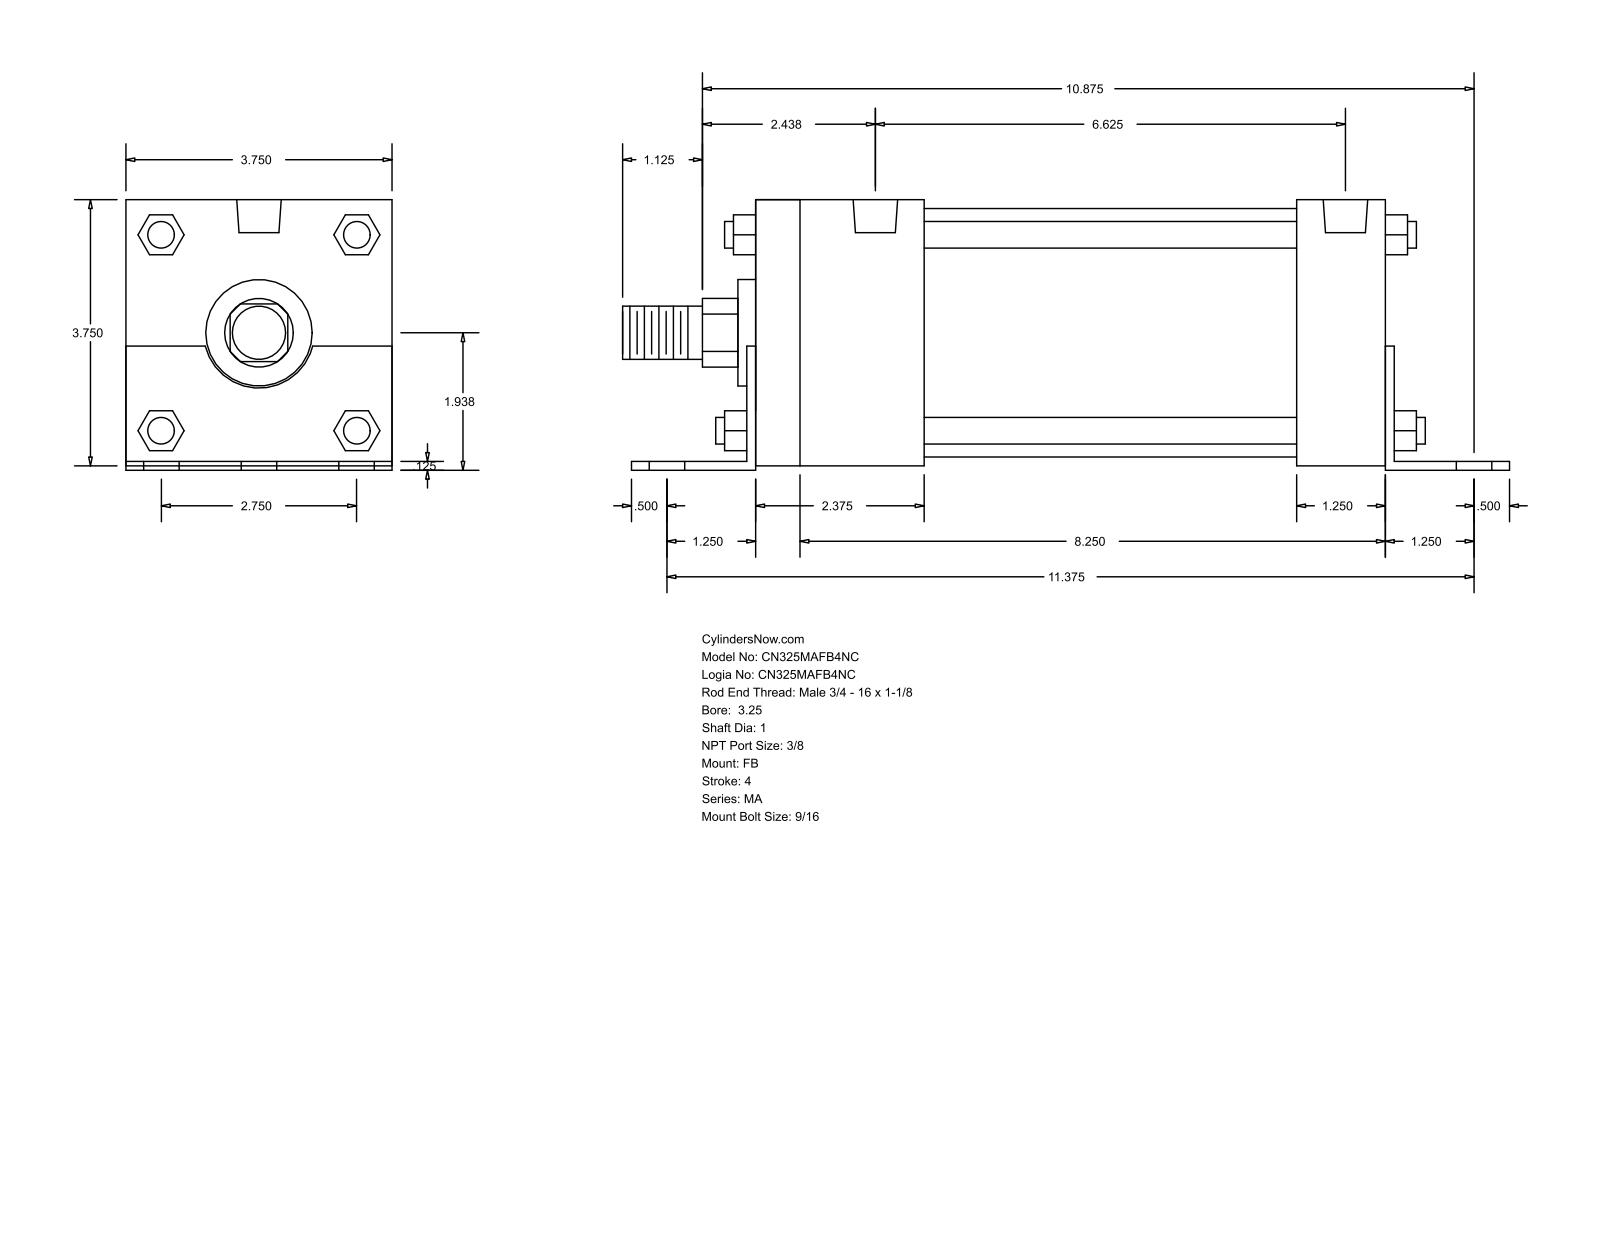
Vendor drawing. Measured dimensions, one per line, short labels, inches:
name: MA_FB__0325_1
written by: GSSL Pune (CONFIG_CONTROL_DESIGN)
unit: in
bodies: 0 solids, 140 faces (105 planar, 35 cylindrical, 0 other)
size: 12.5 × 3.813 × 3.75
holes: 6× ⌀0.563, 4× ⌀0.437, 2× ⌀0.627
bosses: 4× ⌀0.375, 1× ⌀3.5, 1× ⌀1.5, 1× ⌀1, 1× ⌀0.75
rounds: 1× R0.484, 1× R0.78
face distances: 3.75, 0.125, 0.063, 3.812, 0.062, 3.687, 0.125, 8.875, 9.125, 9
hole spacings: 1.375, 11.458, 11.375, 0.187, 2.275, 2.427, 2.75, 3.243
